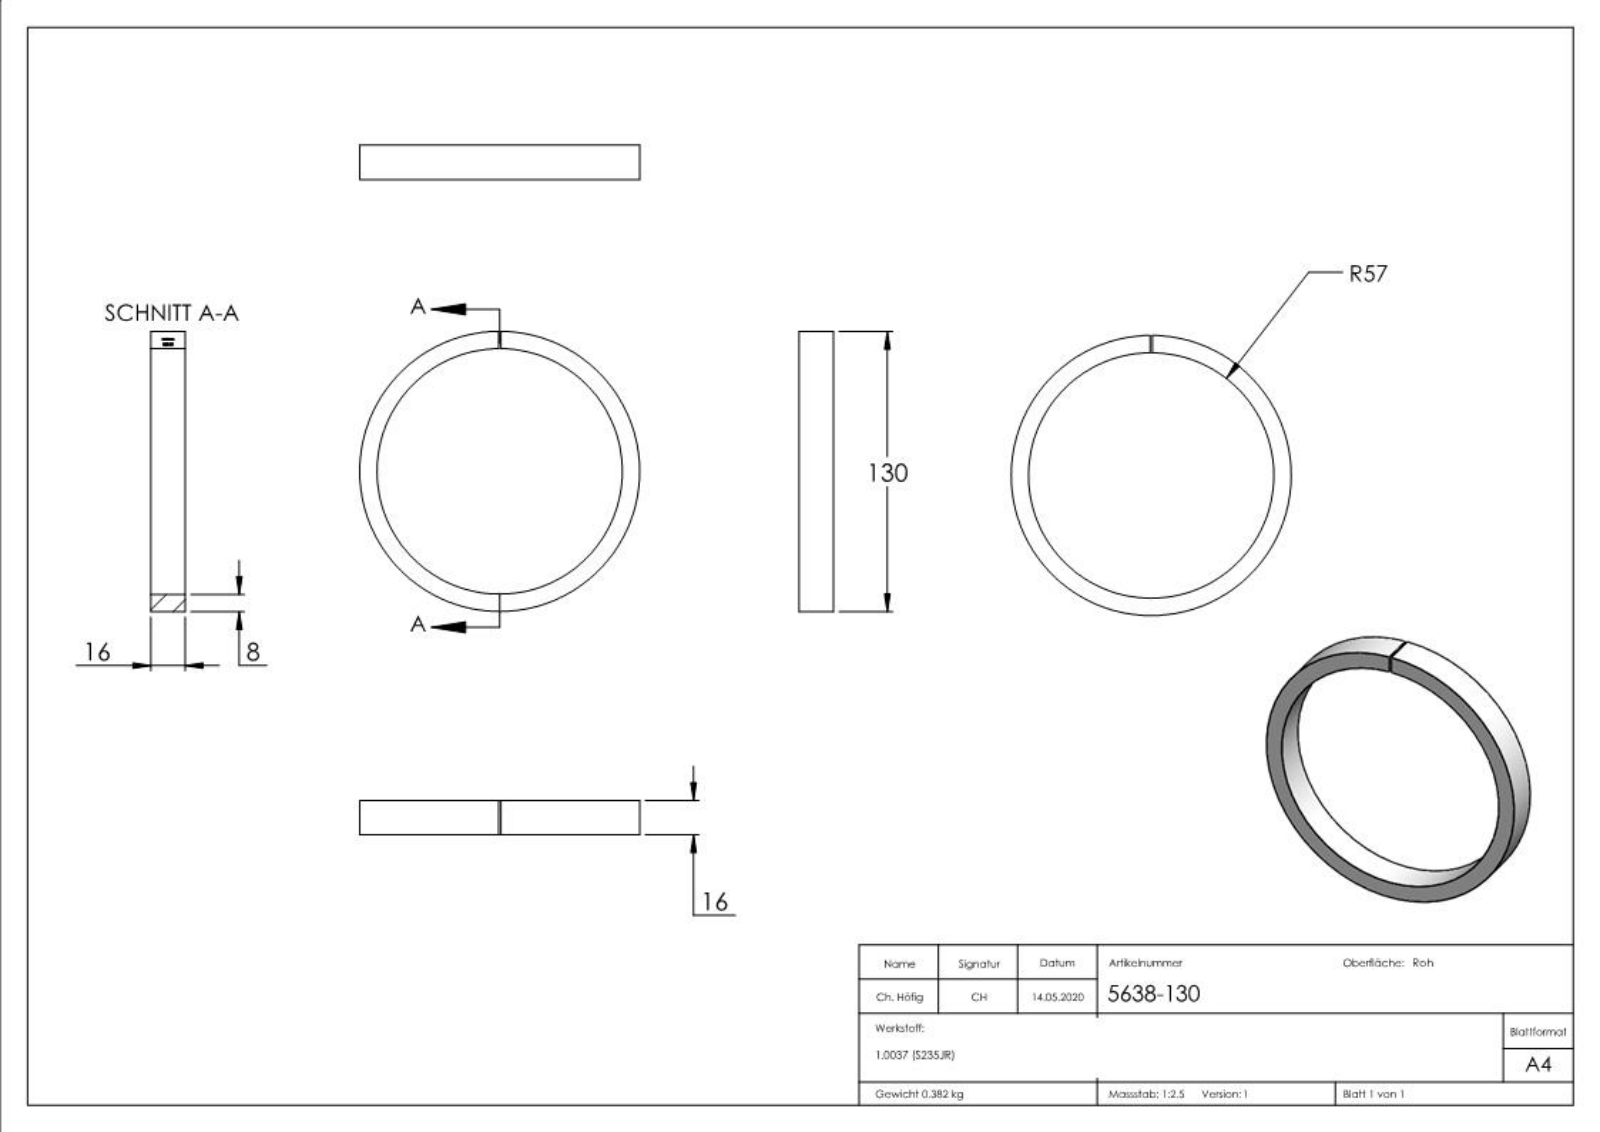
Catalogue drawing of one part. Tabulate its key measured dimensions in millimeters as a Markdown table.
| quantity | value |
| --- | --- |
| part name | 5638-130 |
| STEP written by | SolidWorks 2015 (CONFIG_CONTROL_DESIGN) |
| units | millimeters |
| bodies | 1 solid, 227 faces (106 planar, 2 cylindrical, 119 other) |
| overall size | 130 × 130 × 16 |
| volume | 48 931 mm³ |
| surface area | 18 611 mm² |
| round holes (diameter × count) | 114 × 1 |
| round bosses / shafts (diameter × count) | 130 × 1 |
| main face-to-face distances | 16, 1, 1.1, 1.78, 0.83, 2.45, 2.12, 0.99, 2.77, 1.21 |
